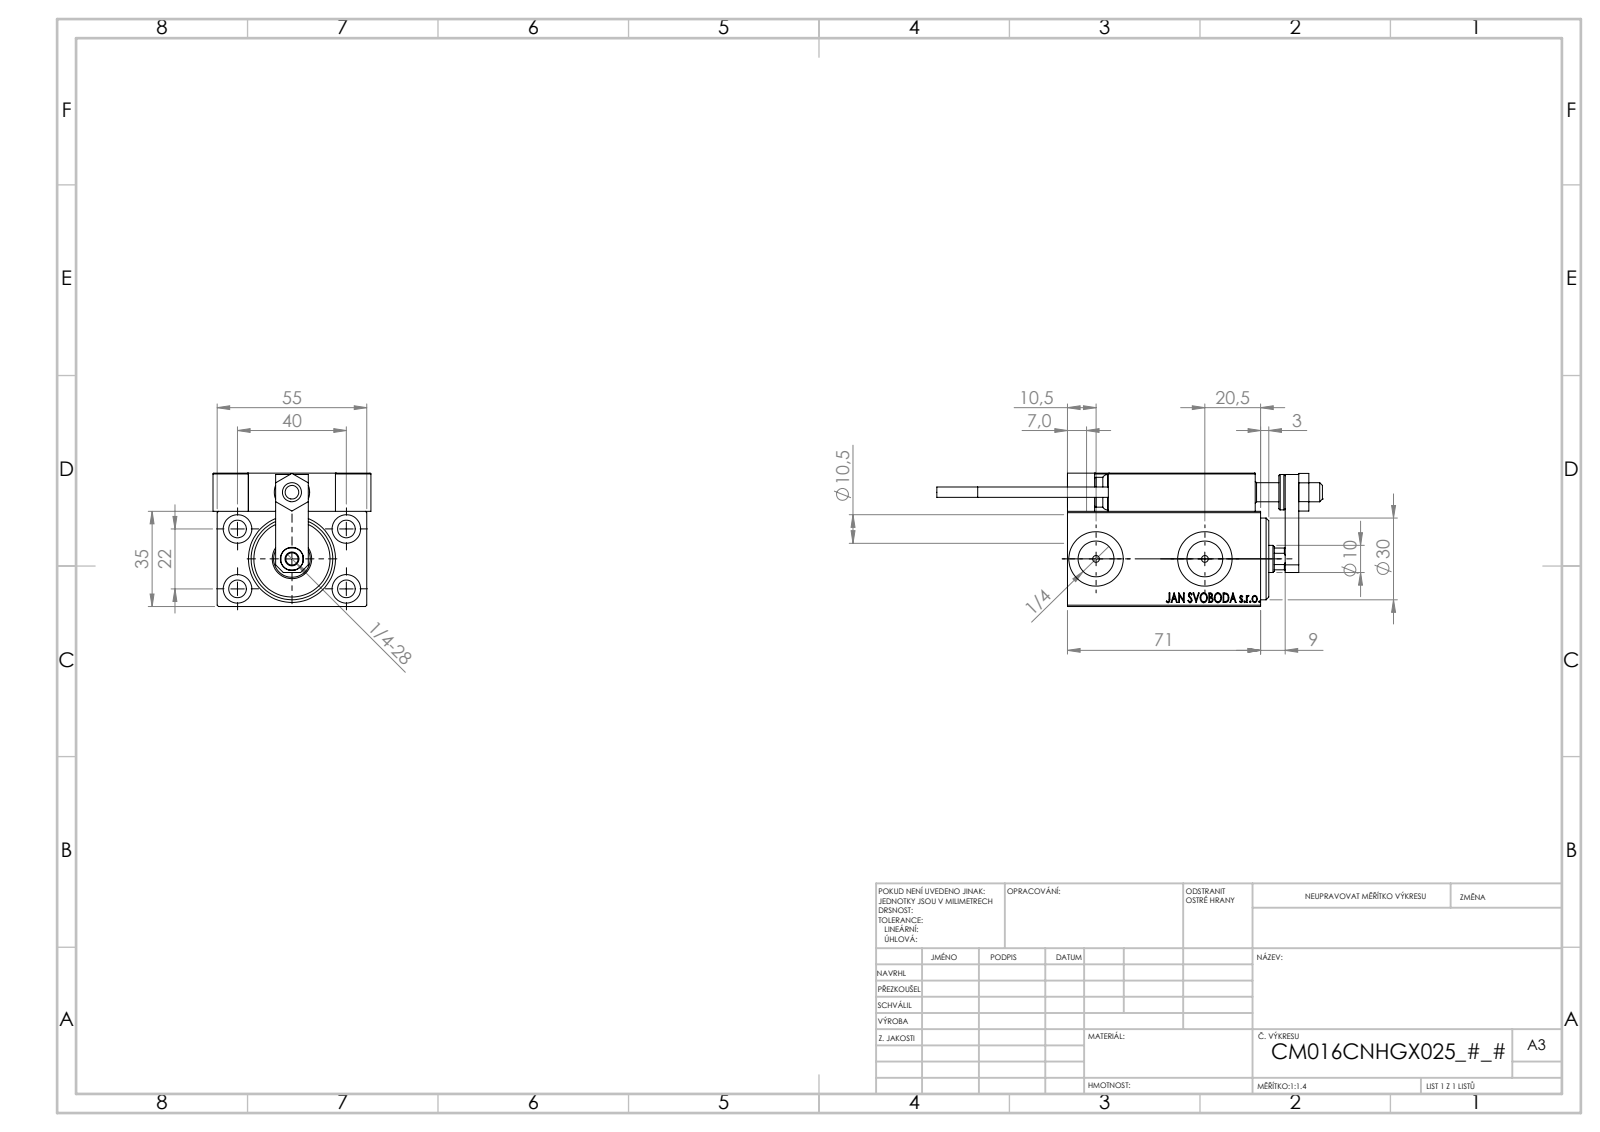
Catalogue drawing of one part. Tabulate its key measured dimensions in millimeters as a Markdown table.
| quantity | value |
| --- | --- |
| part name | Block; V450CM_VC_B; V450CM_C_Body; SWITCH DIM B,W (+7 more) |
| STEP written by | SolidWorks 2019 (CONFIG_CONTROL_DESIGN) |
| units | millimeters |
| bodies | 23 solids, 1285 faces (561 planar, 190 cylindrical, 534 other) |
| overall size | 141.7 × 58 × 49 |
| volume | 161 787 mm³ |
| surface area | 55 364 mm² |
| round holes (diameter × count) | 8 × 5, 3.2 × 4, 4 × 4, 6.5 × 4, 10.5 × 4, 2.5 × 2, 5 × 2, 13.16 × 2, 20 × 2, 4.5 × 1, 7 × 1, 8.5 × 1 |
| round bosses / shafts (diameter × count) | 5 × 2, 3.8 × 2, 13 × 1, 11 × 1 |
| partial cylindrical surfaces (radius × count) | 0.3 × 30, 3 × 2, 4.5 × 1 |
| main face-to-face distances | 35, 5, 49, 14, 10, 7, 3, 55, 1.5, 59 |
| hole center spacings | 22.83, 40, 11.37, 20, 22, 23.09, 24.13, 29.59 |
